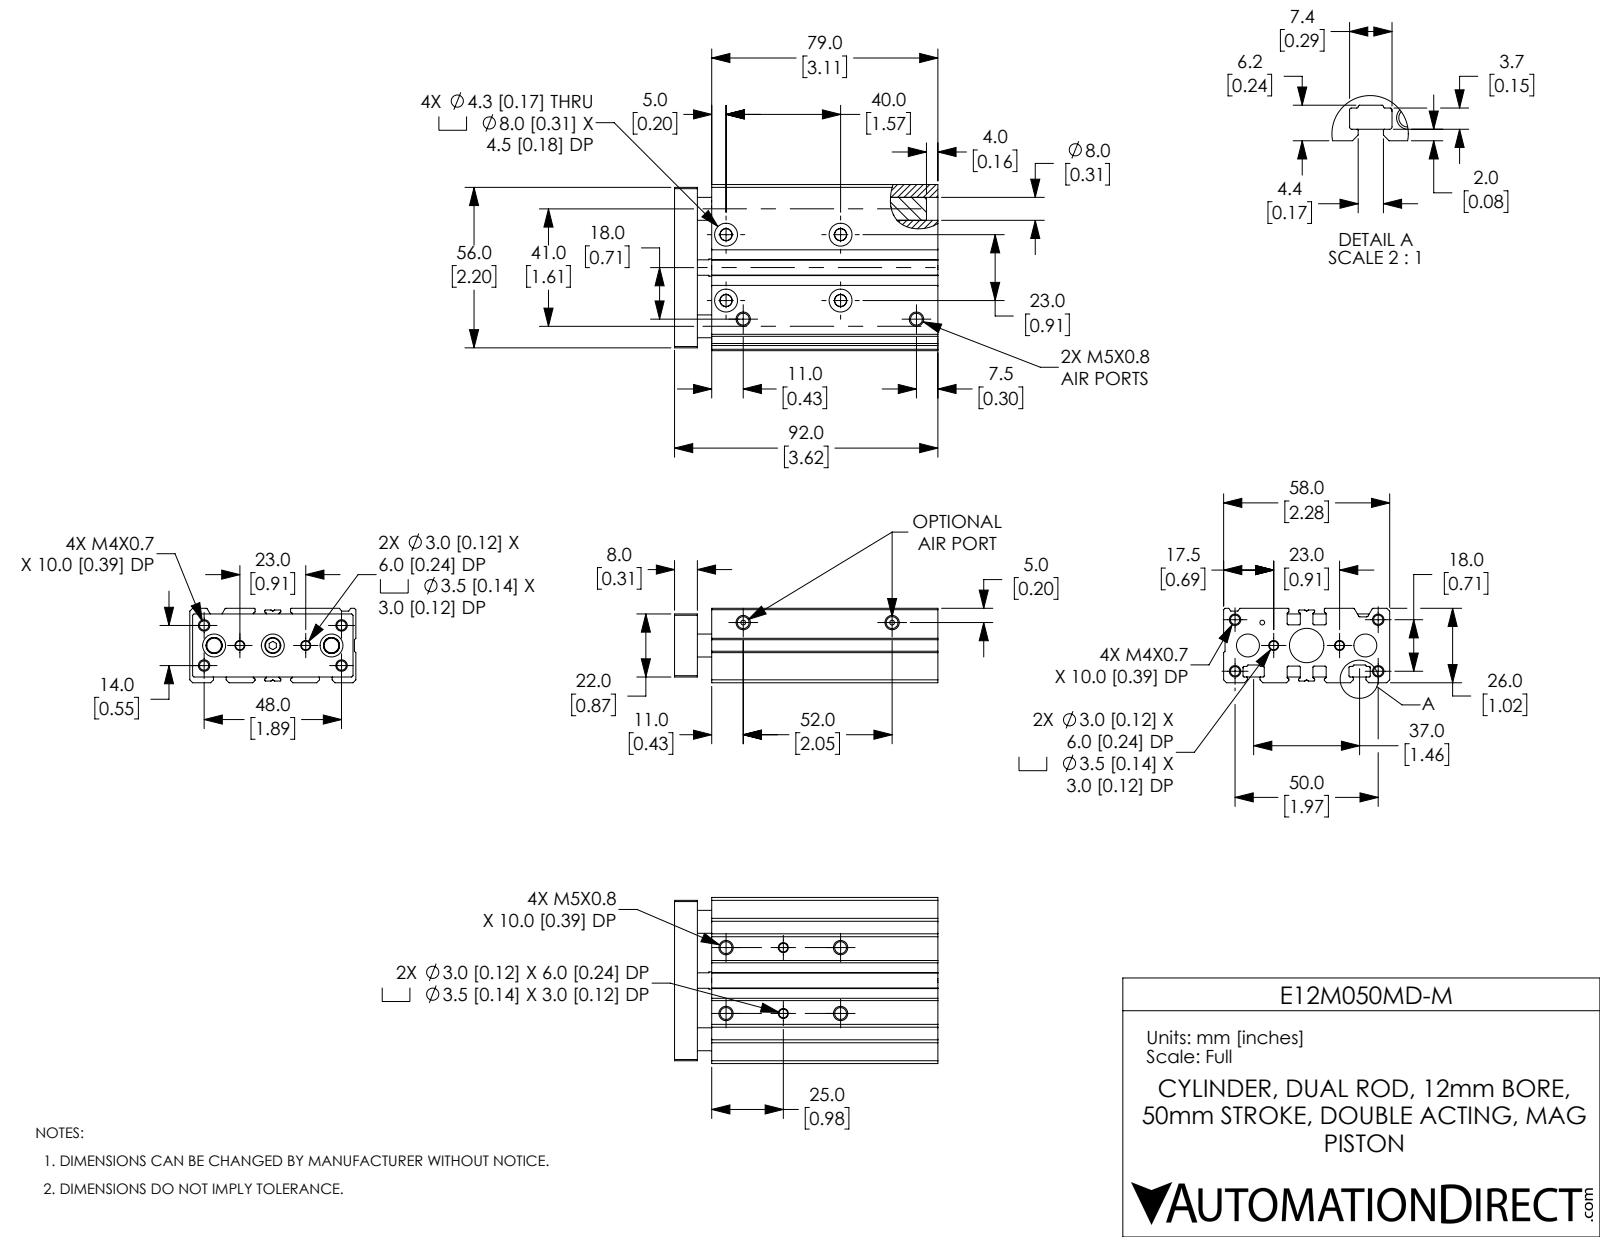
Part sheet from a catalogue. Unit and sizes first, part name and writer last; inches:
Units: inches
Overall size (bounding box): 3.622 × 2.283 × 1.024
Round holes (diameter × count): ⌀0.128 ×8, ⌀0.163 ×8, ⌀0.315 ×7, ⌀0.118 ×4, ⌀0.138 ×4, ⌀0.169 ×4, ⌀0.066 ×3, ⌀0.157 ×3, ⌀0.22 ×2, ⌀0.315 ×1, ⌀0.472 ×1, ⌀0.472 ×1
Round bosses / shafts (diameter × count): ⌀0.236 ×1, ⌀0.22 ×1
Partial cylindrical surfaces — rounded edges, fillets, slot ends (radius × count): R0.016 ×20, R0.008 ×18, R0.01 ×8, R0.012 ×6, R0.02 ×4
Main face-to-face distances: 1.024, 0.228, 2.283, 0.315, 0.079, 0.354, 0.512, 0.795, 0.945, 1.055
Hole centre spacings: 0.088, 0.308, 0.396, 0.564, 0.631, 0.639, 0.787, 0.906
Volume: 6.385 in³ · Surface area: 66.73 in²
Bodies: 5 solids, 413 faces (137 planar, 188 cylindrical, 88 other)
Part name (STEP PRODUCT): E12M050MD-M; E12M050MD-D_BODY; E12M050MD-M_ENDPLATE
STEP written by: SolidWorks 2019 (CONFIG_CONTROL_DESIGN)
